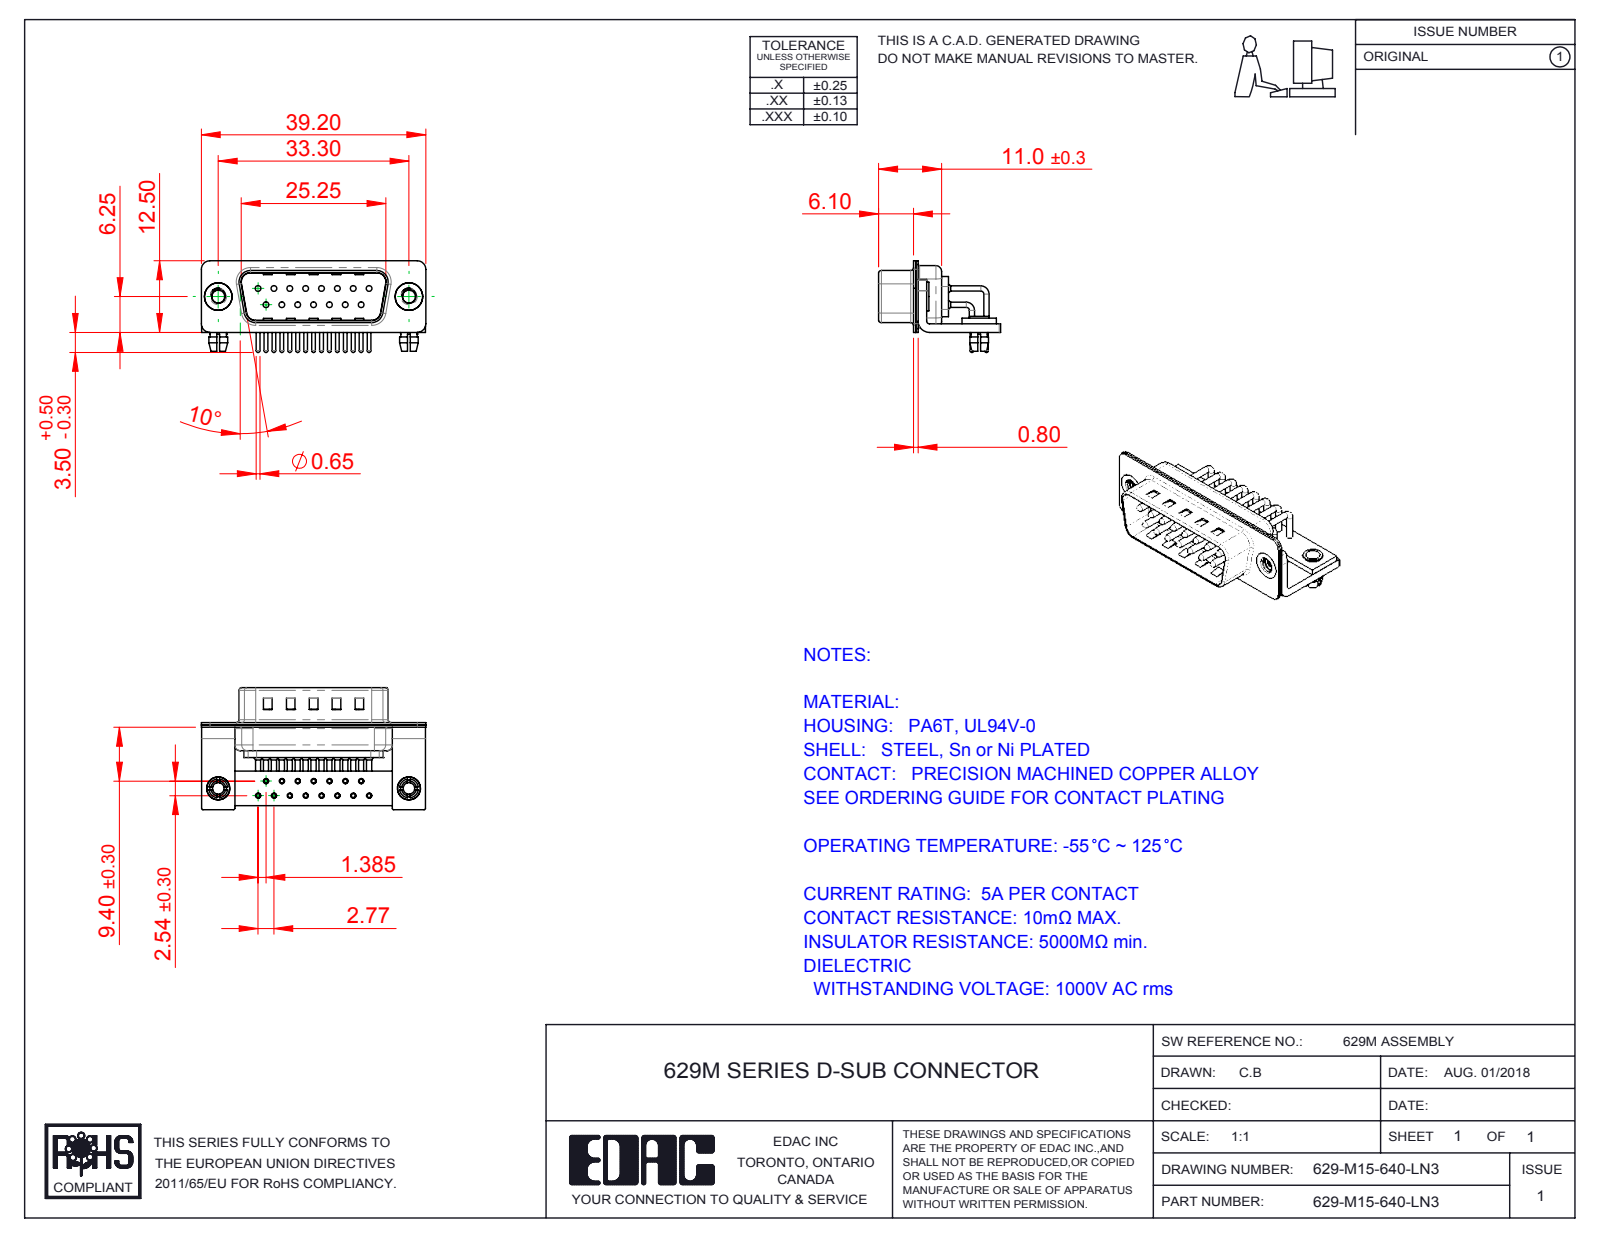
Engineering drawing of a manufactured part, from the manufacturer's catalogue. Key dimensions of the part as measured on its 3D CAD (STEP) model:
Part name (STEP PRODUCT): 629M Contact Row 2; 629M Stabilizer Bracket; 629-M15-640-LN3; 629M Stabilizer Board_15 Contacts (+6 more)
STEP written by: SolidWorks 2016 (CONFIG_CONTROL_DESIGN)
Units: millimetres
Bodies: 25 solids, 2162 faces (1173 planar, 757 cylindrical, 232 other)
Overall size (bounding box): 39.2 × 21.3 × 16
Volume: 2 481 mm³ · Surface area: 6 762 mm²
Round holes (diameter × count): ⌀2 ×17, ⌀0.9 ×15, ⌀1 ×15, ⌀1.7 ×15, ⌀2.26 ×2, ⌀2.5 ×2, ⌀3.2 ×2, ⌀4 ×2, ⌀4.8 ×2
Round bosses / shafts (diameter × count): ⌀0.9 ×21, ⌀1.5 ×15, ⌀0.65 ×15, ⌀5 ×2, ⌀4.9 ×2, ⌀4 ×2, ⌀3.4 ×2, ⌀3.3 ×2
Partial cylindrical surfaces — rounded edges, fillets, slot ends (radius × count): R0.25 ×16, R1.5 ×16, R1.01 ×15, R2 ×13, R0.5 ×9, R1.6 ×8, R0.6 ×4, R0.65 ×4
Main face-to-face distances: 0.4, 1.5, 0.85, 0.8, 1.25, 10.4, 9.55, 1, 1.9, 9.15
Hole centre spacings: 2.77, 5.54, 3.16, 8.31, 4.87, 11.08, 2.89, 7.37
